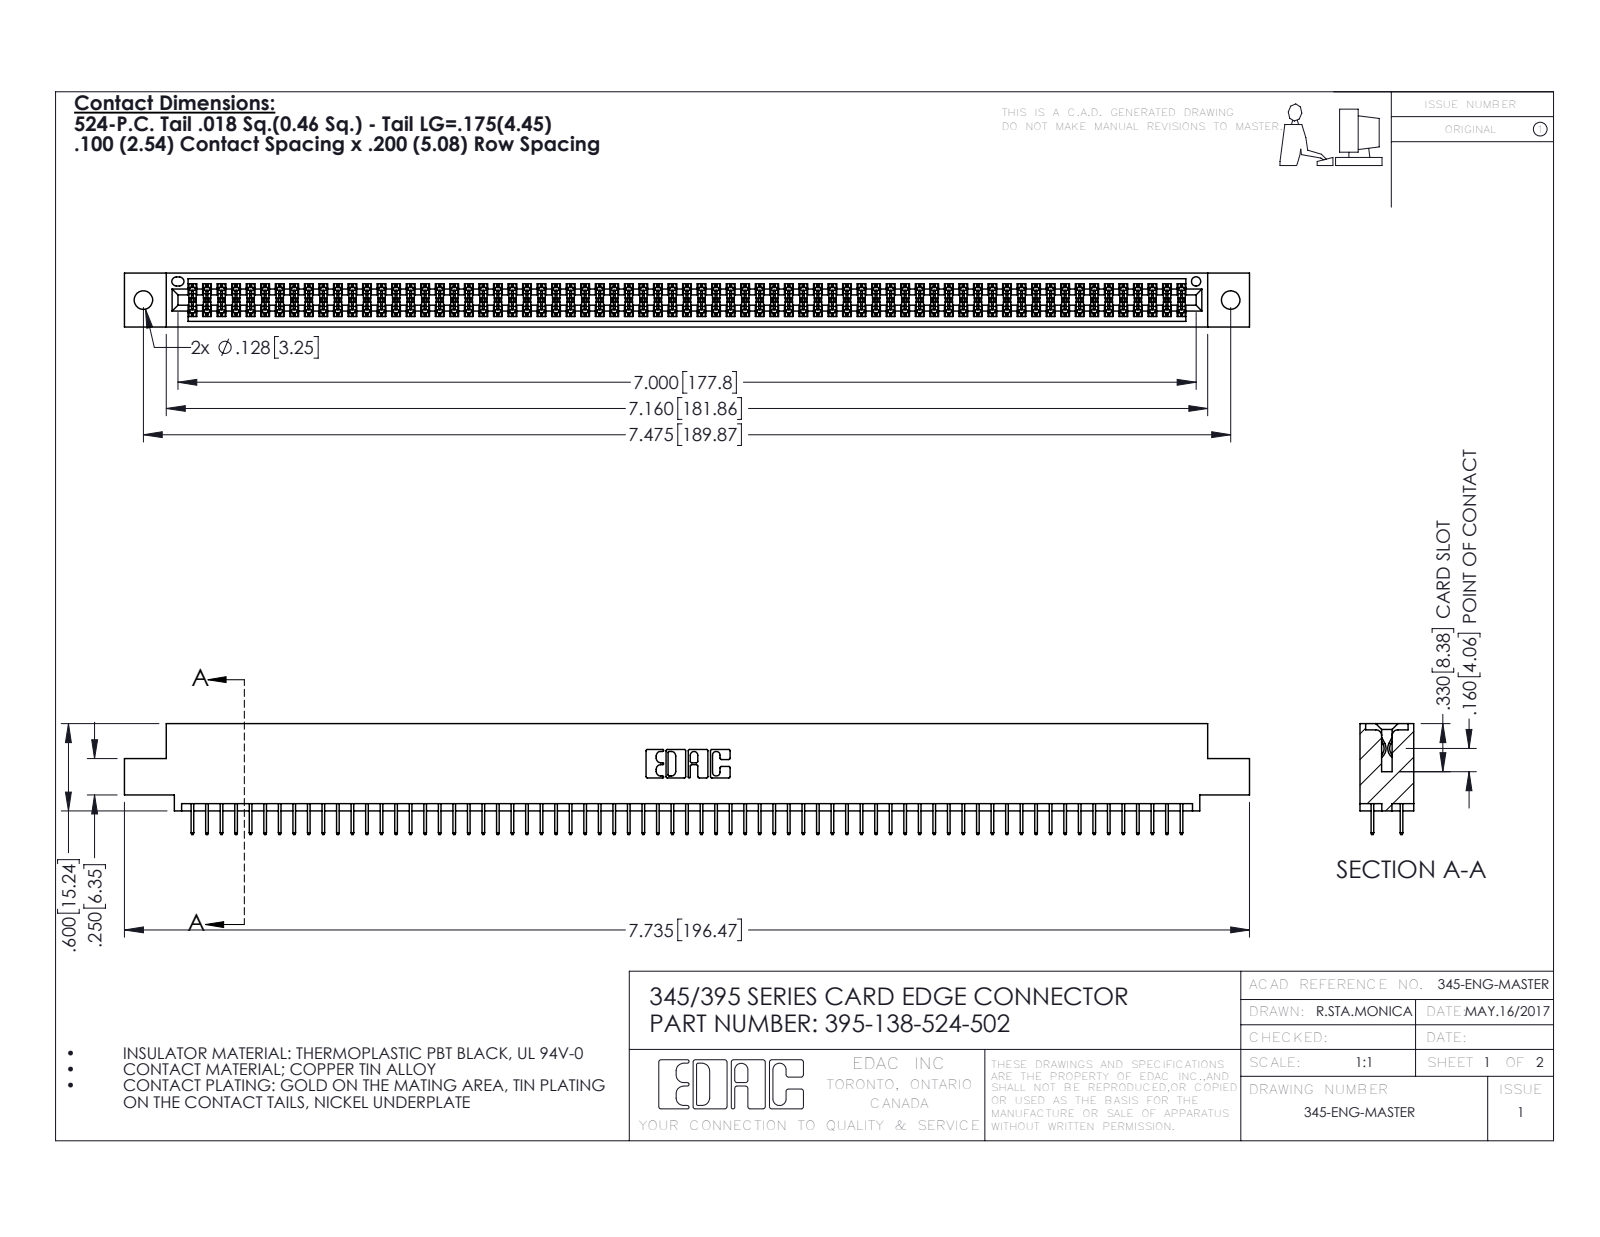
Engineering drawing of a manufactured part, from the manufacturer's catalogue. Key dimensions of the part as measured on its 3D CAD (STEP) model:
Part name (STEP PRODUCT): 395-138-524-502; 345-292-001_345-293-124; 345 Part_0.110 Offset - 0.128 Dia
STEP written by: SolidWorks 2016 (CONFIG_CONTROL_DESIGN)
Units: inches
Bodies: 139 solids, 7582 faces (5466 planar, 2116 cylindrical, 0 other)
Overall size (bounding box): 7.735 × 0.762 × 0.37
Volume: 1.16 in³ · Surface area: 43.25 in²
Round holes (diameter × count): ⌀0.128 ×2, ⌀0.064 ×1
Partial cylindrical surfaces — rounded edges, fillets, slot ends (radius × count): R0.006 ×207, R0.01 ×22, R0.007 ×6, R0.031 ×6, R0.026 ×3, R0.014 ×2, R0.019 ×2, R0.022 ×2
Main face-to-face distances: 0.072, 0.298, 0.2, 0.37, 0.098, 0.272, 0.025, 0.225, 0.072, 0.175
Hole centre spacings: 0.27, 7.239, 7.475
